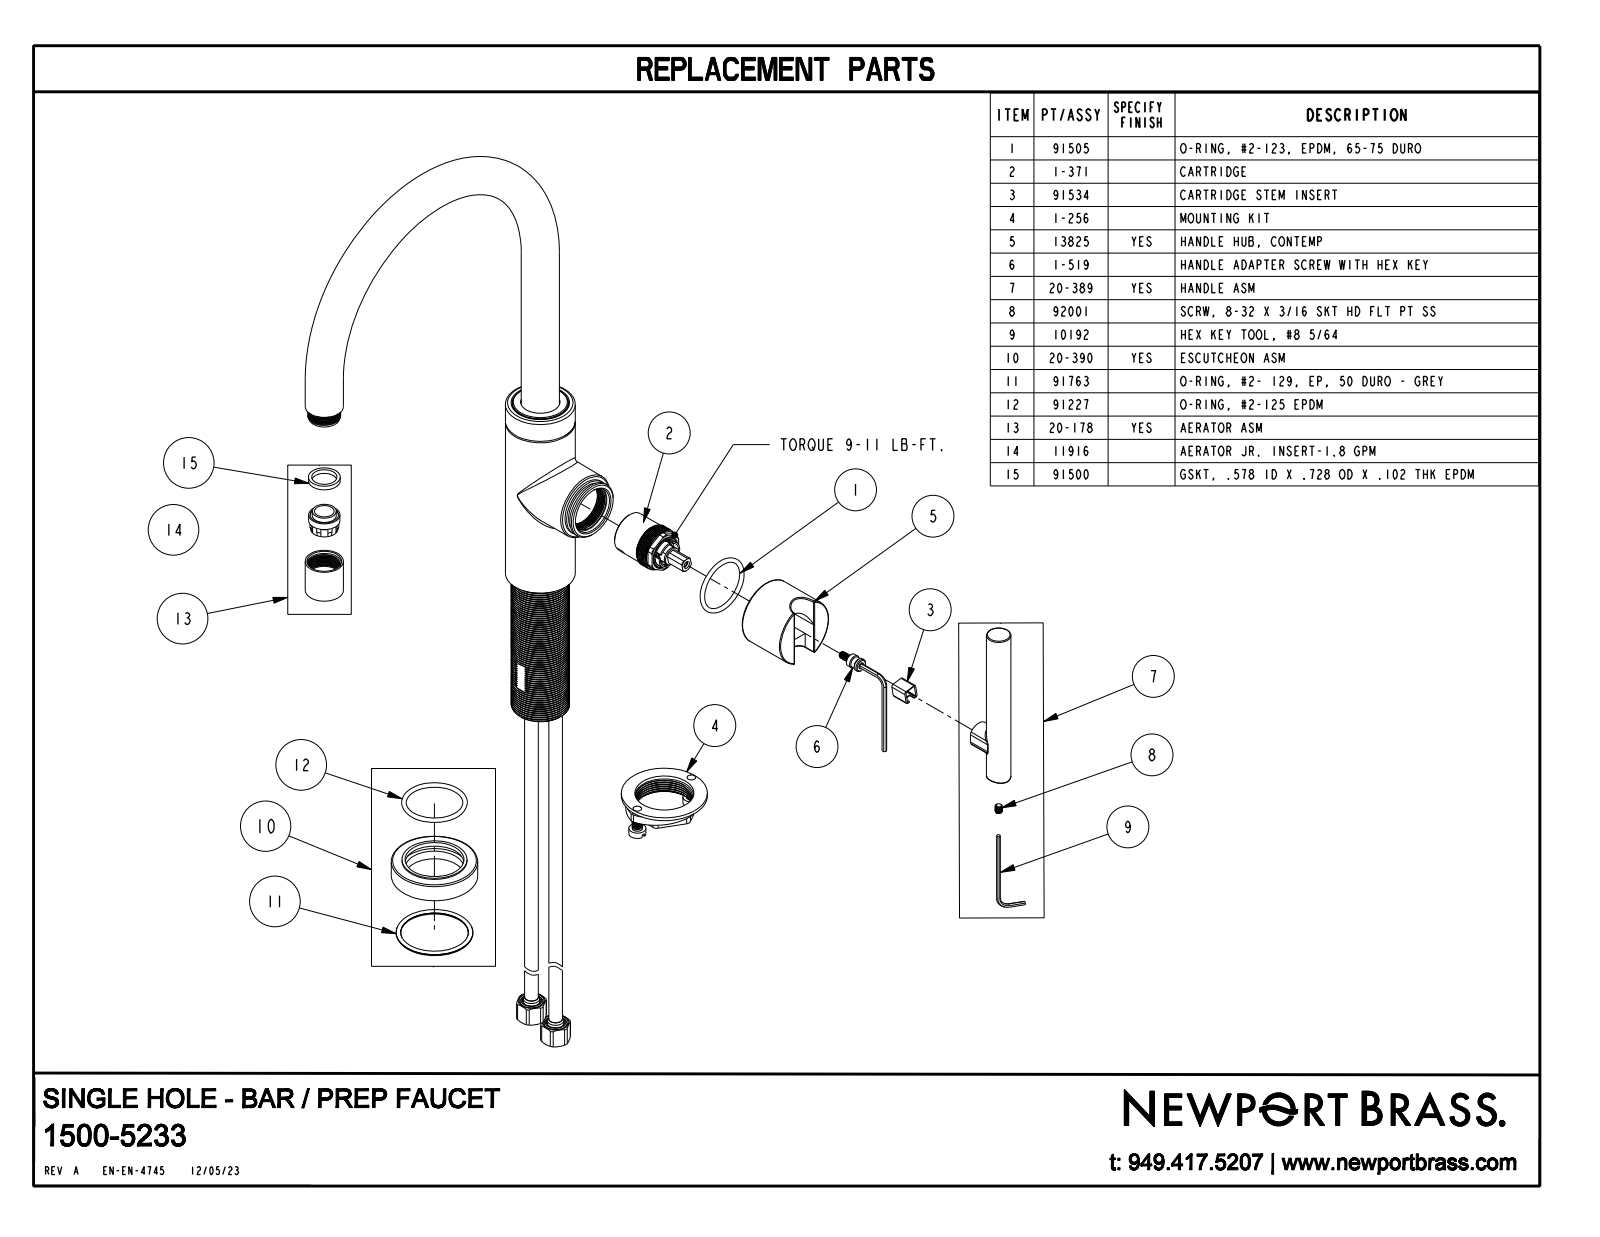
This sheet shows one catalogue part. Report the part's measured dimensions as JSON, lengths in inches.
{"part_name": "1500-5233_SW0001", "step_written_by": "CREO PARAMETRIC BY PTC INC, 2023134 (CONFIG_CONTROL_DESIGN)", "units": "inches", "bodies": {"solids": 2, "faces": 142, "planar": 37, "cylindrical": 51, "other": 54}, "overall_size": [13.35, 8.554, 4.007], "volume_in3": 25.68, "surface_area_in2": 100, "round_holes": [[0.56, 1], [0.691, 1], [0.9, 1]], "round_bosses_or_shafts": [[0.875, 2], [1.98, 1], [1.6, 1], [1.58, 1], [1.473, 1], [1.28, 1], [0.56, 1]], "partial_cylinders_radius": [[0.02, 6], [0.12, 4], [0.313, 4], [0.06, 2], [0.297, 1], [0.31, 1], [0.9, 1]], "face_to_face_distances": [0.425, 5.226, 4.801, 0.724, 0.02, 0.625, 5.206, 4.781, 0.063, 0.661], "hole_center_spacings": [7.126]}
